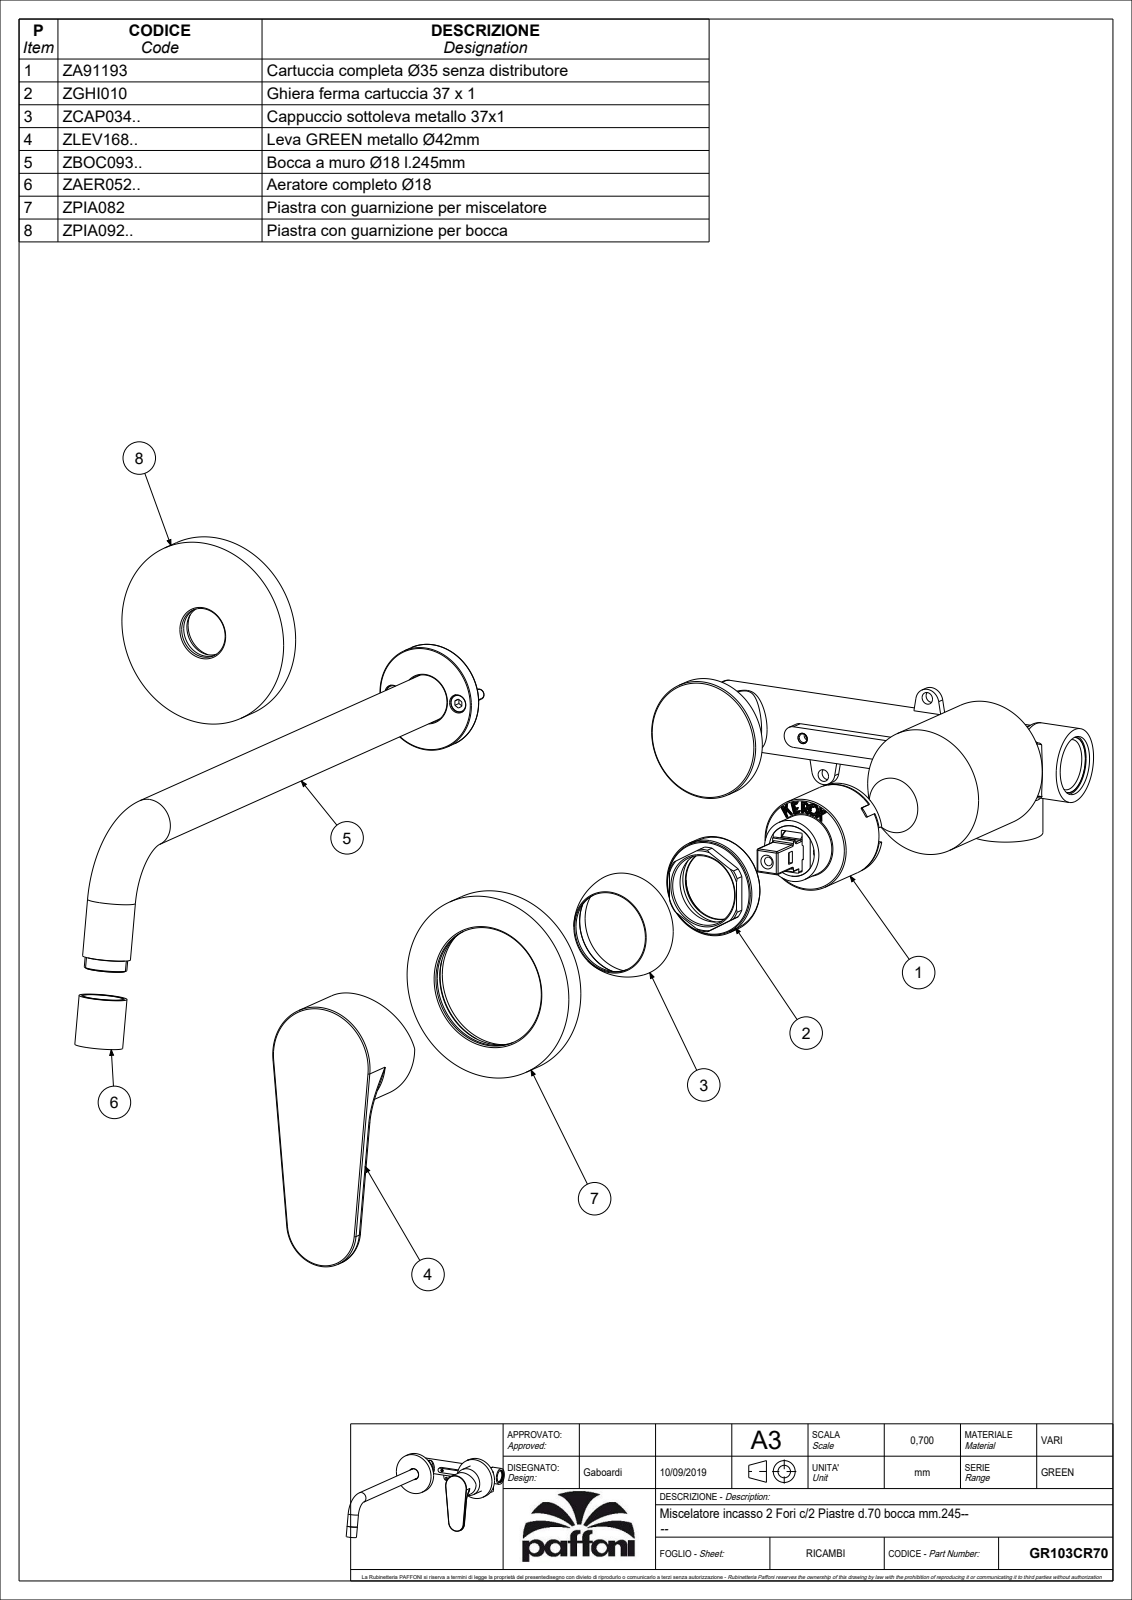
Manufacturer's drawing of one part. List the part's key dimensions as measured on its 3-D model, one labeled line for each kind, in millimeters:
Part name (STEP PRODUCT): GR103CR70
STEP written by: CREO PARAMETRIC BY PTC INC, 2020044 (CONFIG_CONTROL_DESIGN)
Units: millimetres
Bodies: 3 solids, 303 faces (187 planar, 77 cylindrical, 39 other)
Overall size (bounding box): 252.58 × 179 × 114.5
Volume: 178 981 mm³ · Surface area: 65 228 mm²
Round holes (diameter × count): ⌀3 ×1, ⌀3.4 ×1, ⌀4.2 ×1, ⌀4.6 ×1, ⌀19.5 ×1, ⌀30.6 ×1, ⌀32.4 ×1, ⌀36 ×1, ⌀37.5 ×1, ⌀39 ×1
Round bosses / shafts (diameter × count): ⌀70 ×2, ⌀18 ×2, ⌀44.8 ×1, ⌀42 ×1, ⌀35 ×1, ⌀23.5 ×1, ⌀7.6 ×1, ⌀5.5 ×1
Partial cylindrical surfaces — rounded edges, fillets, slot ends (radius × count): R0.5 ×2, R1.2 ×2, R3 ×2, R0.65 ×1, R0.9 ×1, R0.95 ×1, R1.5 ×1, R14.75 ×1
Main face-to-face distances: 9, 66.5, 57.5, 6, 60.5, 51.5, 2.5, 3.5, 64, 55
Hole centre spacings: 14.64
